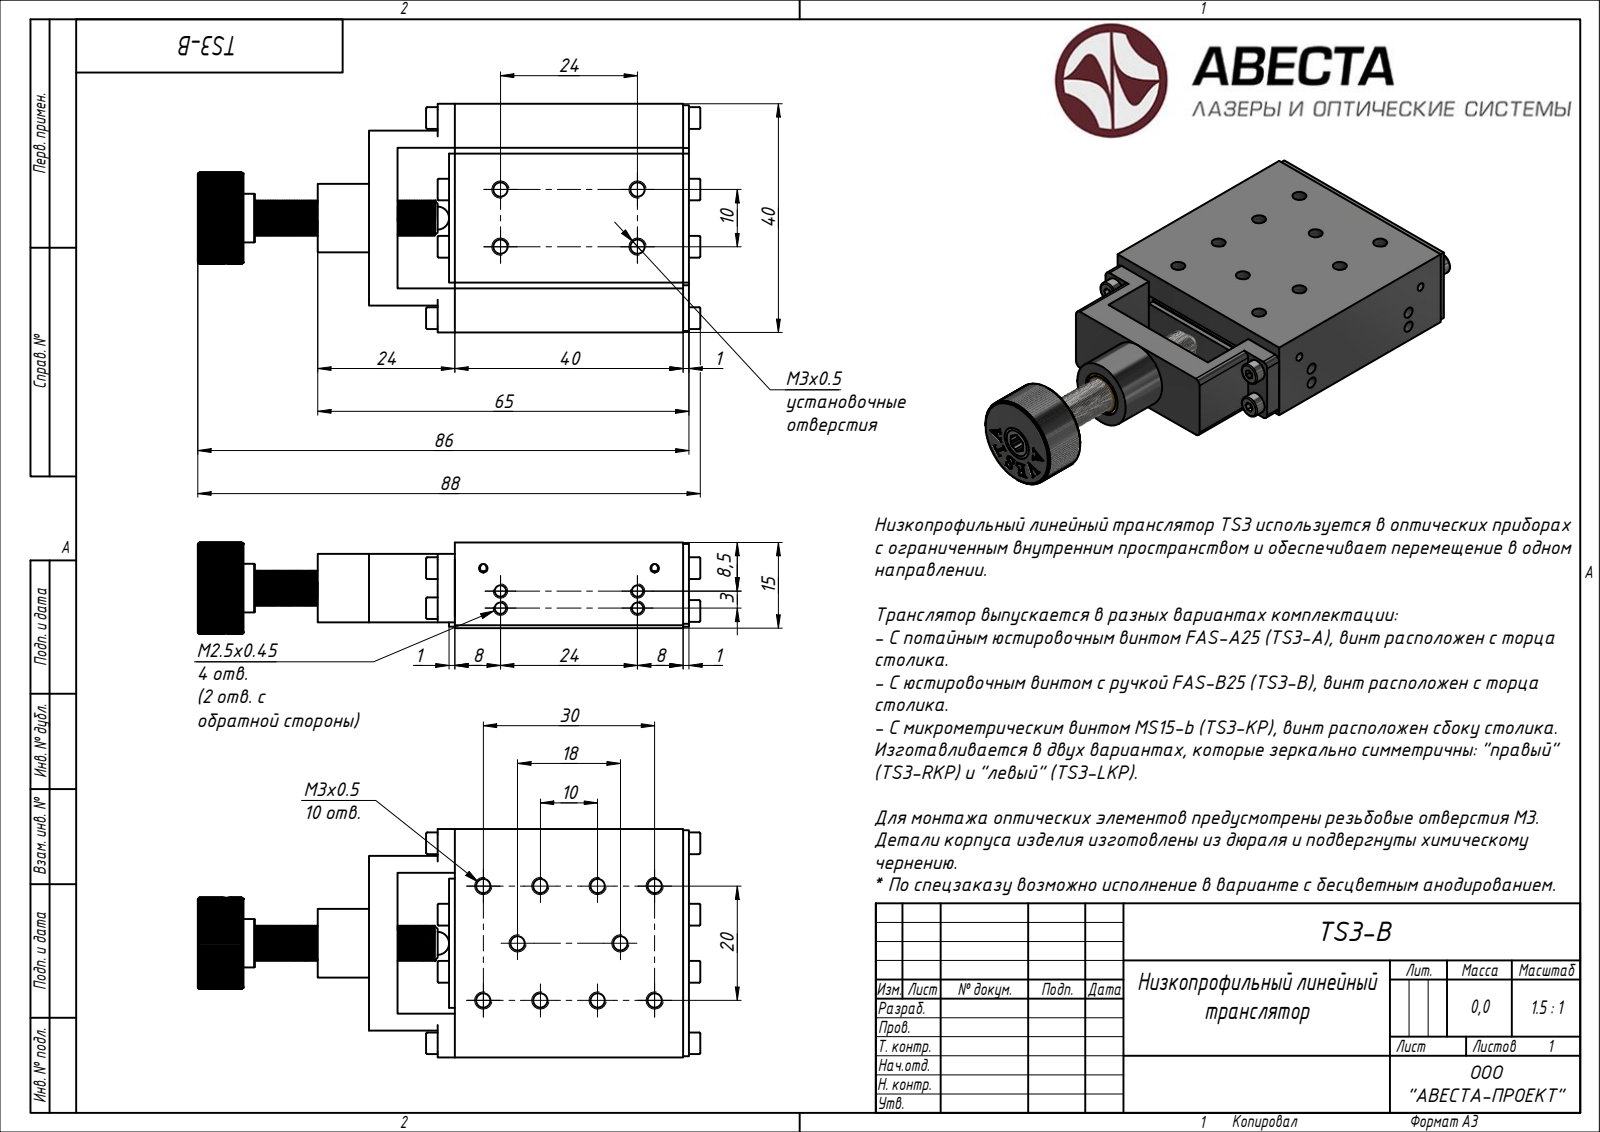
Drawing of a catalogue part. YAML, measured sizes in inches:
step_written_by: "Rhino 7.34 (AUTOMOTIVE_DESIGN)"
units: inches
bodies: {solids: 6, faces: 1286, planar: 707, cylindrical: 369, other: 210}
overall_size: [3.465, 1.575, 0.63]
volume: 1.578
surface_area: 29.34
round_holes:
  - {diameter: 0.097, count: 15}
  - {diameter: 0.098, count: 5}
  - {diameter: 0.059, count: 4}
  - {diameter: 0.062, count: 4}
  - {diameter: 0.112, count: 4}
  - {diameter: 0.079, count: 2}
  - {diameter: 0.079, count: 2}
  - {diameter: 0.062, count: 1}
  - {diameter: 0.118, count: 1}
  - {diameter: 0.122, count: 1}
  - {diameter: 0.236, count: 1}
  - {diameter: 0.315, count: 1}
round_bosses_or_shafts:
  - {diameter: 0.15, count: 6}
  - {diameter: 0.079, count: 5}
  - {diameter: 0.118, count: 3}
  - {diameter: 0.472, count: 1}
  - {diameter: 0.354, count: 1}
  - {diameter: 0.335, count: 1}
  - {diameter: 0.236, count: 1}
partial_cylinders:
  - {radius: 0.039, count: 8}
  - {radius: 0.079, count: 4}
  - {radius: 0.043, count: 2}
  - {radius: 0.048, count: 1}
  - {radius: 0.048, count: 1}
  - {radius: 0.315, count: 1}
face_to_face_distances: [0.02, 0.197, 0.374, 0.079, 0.276, 0.118, 0.394, 0.354, 0.591, 0.315]
hole_center_spacings: [0.394, 0.23, 0.787, 0.88, 1.024, 0.339, 0.424, 0.459]
